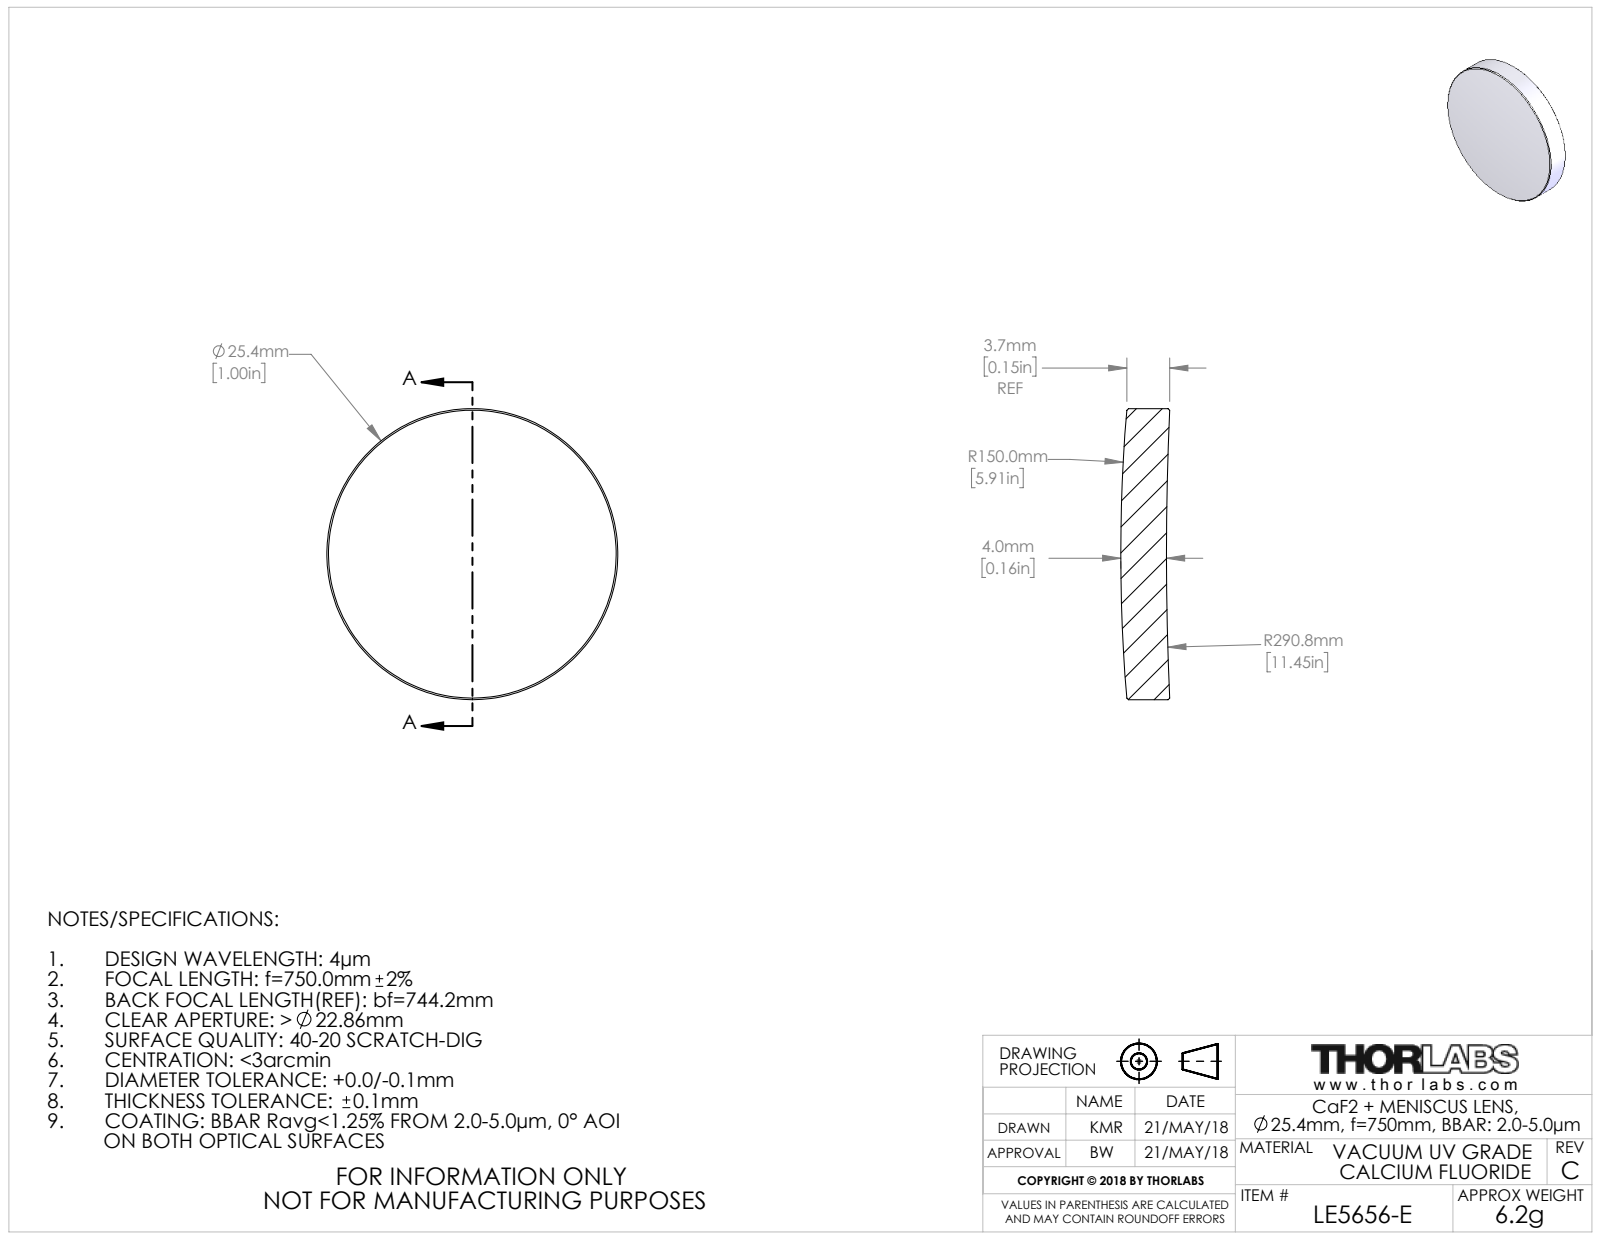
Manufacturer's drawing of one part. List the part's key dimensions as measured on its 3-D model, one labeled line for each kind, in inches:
Part name (STEP PRODUCT): 20167-E0W
STEP written by: SolidWorks 2016 (CONFIG_CONTROL_DESIGN)
Units: inches
Bodies: 1 solid, 10 faces (0 planar, 2 cylindrical, 8 other)
Overall size (bounding box): 1 × 1 × 0.168
Volume: 0.12 in³ · Surface area: 2.015 in²
Round bosses / shafts (diameter × count): ⌀1 ×1
